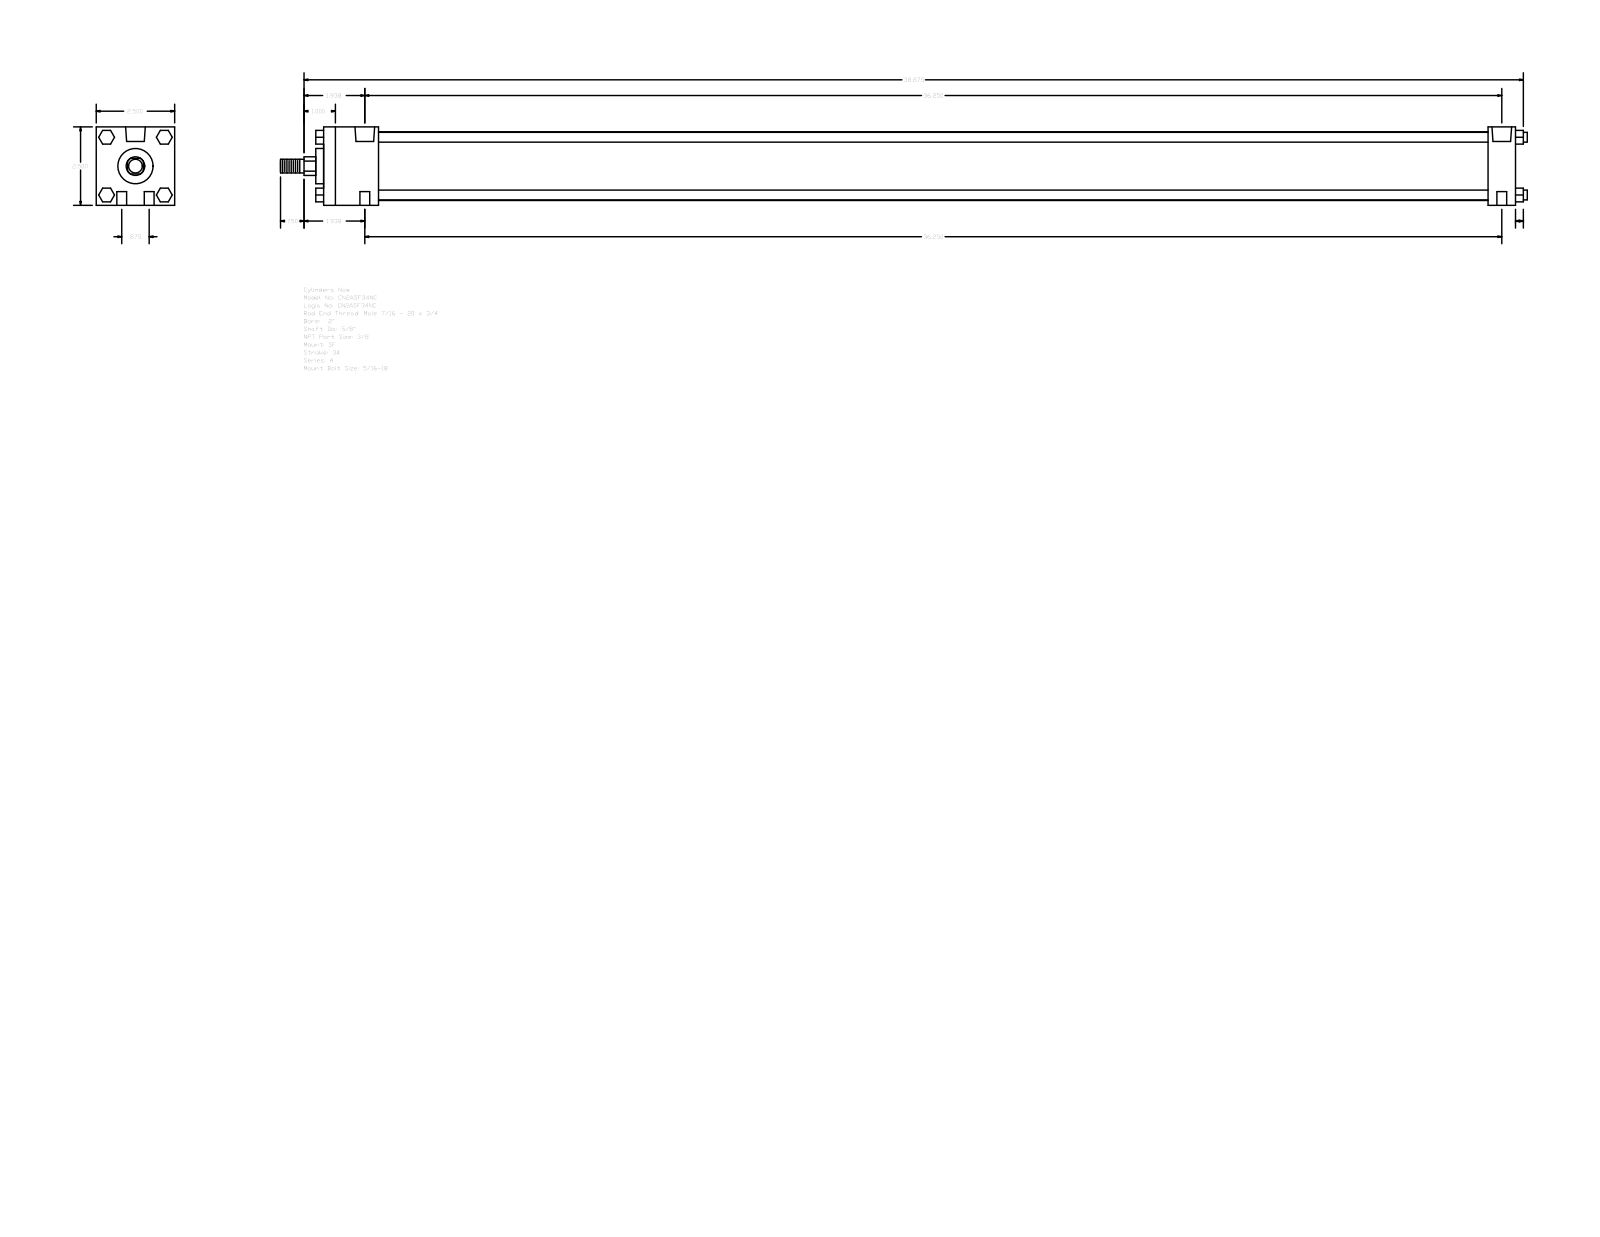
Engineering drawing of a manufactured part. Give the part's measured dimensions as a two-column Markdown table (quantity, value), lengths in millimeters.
| quantity | value |
| --- | --- |
| part name | A_SF__0200_0.625 |
| STEP written by | GSSL Pune (CONFIG_CONTROL_DESIGN) |
| units | millimeters |
| bodies | 0 solids, 124 faces (94 planar, 30 cylindrical, 0 other) |
| overall size | 1009.65 × 63.5 × 63.5 |
| round holes (diameter × count) | 7.94 × 4, 5.56 × 2, 15.93 × 2 |
| round bosses / shafts (diameter × count) | 7.94 × 4, 55.63 × 1, 28.57 × 1, 15.88 × 1, 11.11 × 1 |
| partial cylindrical surfaces (radius × count) | 7.54 × 1 |
| main face-to-face distances | 63.5, 965.2, 942.97, 22.23, 44.45, 898.52, 920.75, 50.8, 6.35, 949.32 |
| hole center spacings | 11.11, 920.82, 920.75, 22.22, 921.02, 912.8 |
